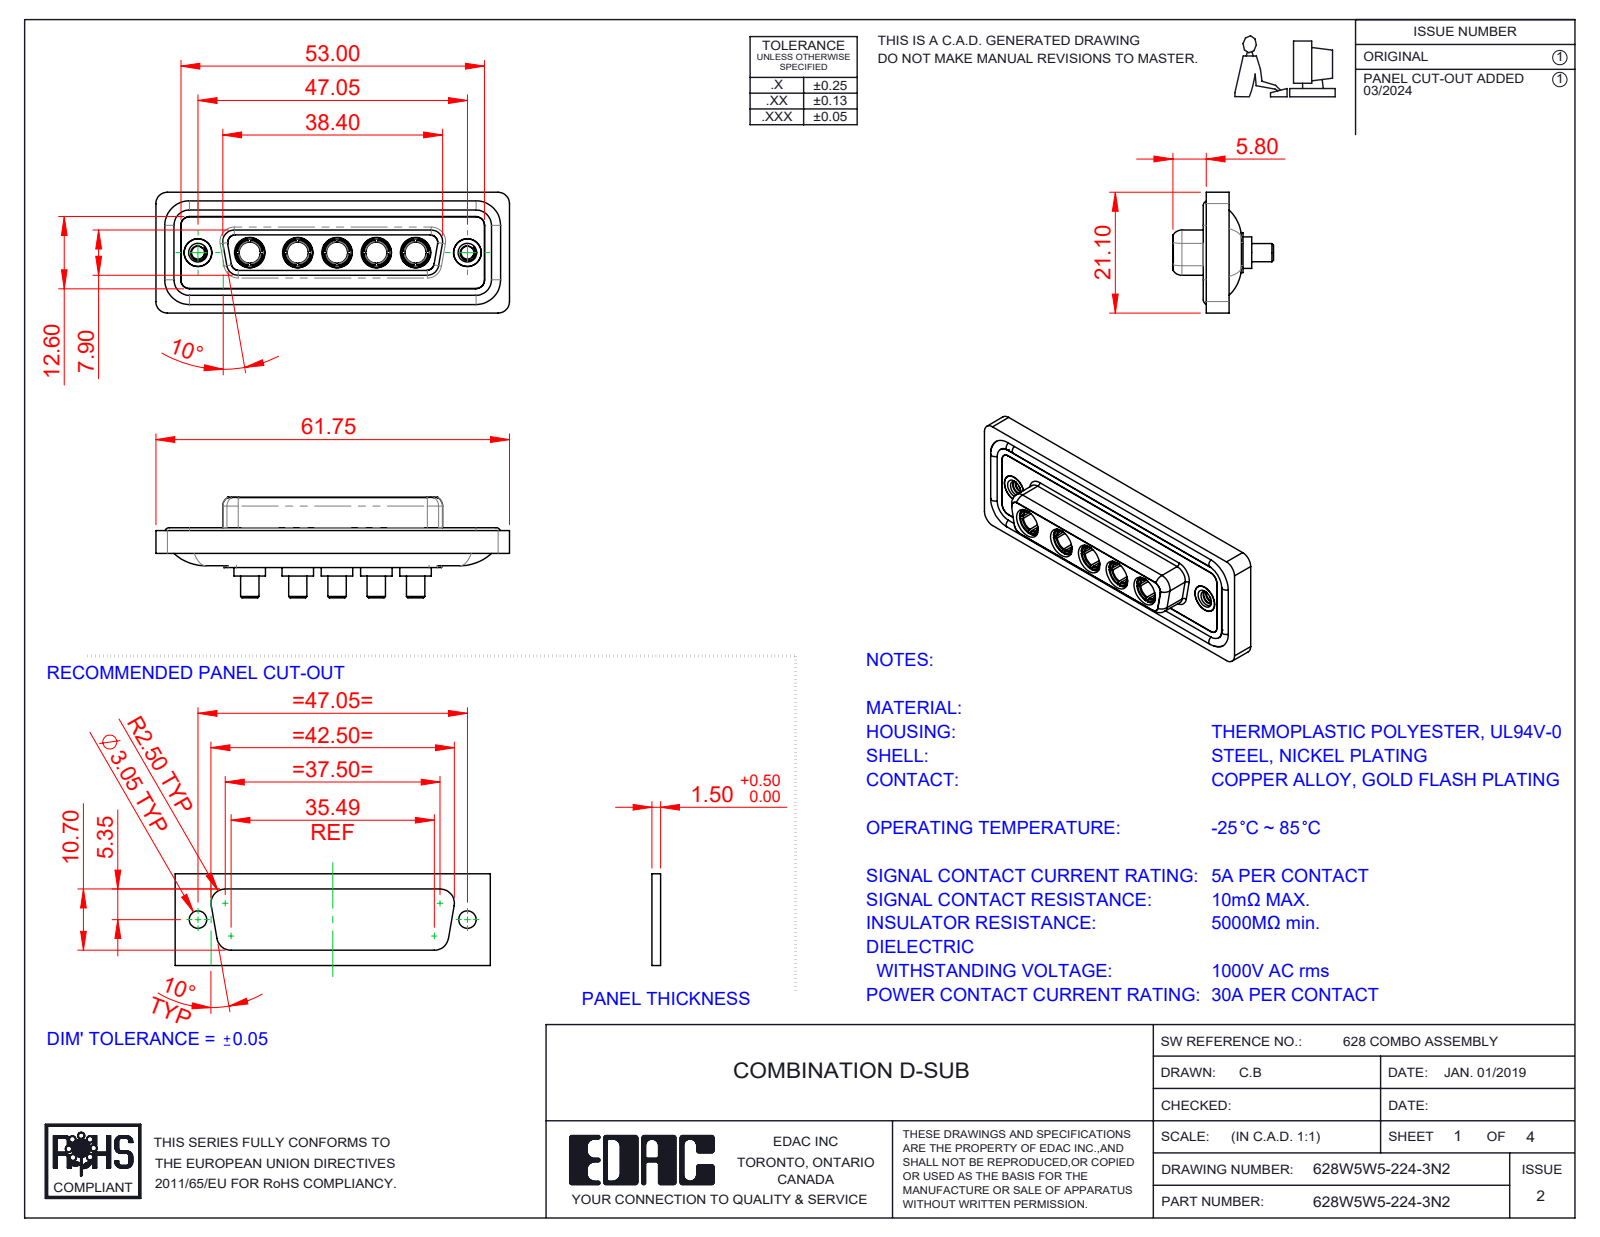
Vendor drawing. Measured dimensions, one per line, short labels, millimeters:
name: 628W5W5-224-3N2; 628Combo Shell Front_25 Contacts; 628Combo Housing_5W5; Power Socket_30A S (+3 more)
written by: SolidWorks 2023 (CONFIG_CONTROL_DESIGN)
unit: mm
bodies: 17 solids, 756 faces (250 planar, 303 cylindrical, 203 other)
size: 61.75 × 21.1 × 17.55
volume: 8 208 mm³; area: 13 438 mm²
holes: 7× ⌀4.85, 5× ⌀3.7, 5× ⌀5.3, 2× ⌀2.26, 2× ⌀4, 2× ⌀4.05, 2× ⌀5
bosses: 5× ⌀5.5, 5× ⌀5.2, 5× ⌀4.96, 5× ⌀4.75, 5× ⌀3.75, 5× ⌀3.2, 4× ⌀1.6, 2× ⌀4.95
rounds: 22× R1.5, 18× R2, 8× R1.35, 8× R1.6, 5× R2.1, 4× R0.25, 4× R0.5, 4× R0.6
face distances: 0.4, 1.8, 7.45, 5.65, 0.5, 7.05, 6.6, 1.6, 1.1, 2.9
hole spacings: 6.86, 9.04, 13.72, 38.01, 8.39, 15.25, 15.9, 17.43
